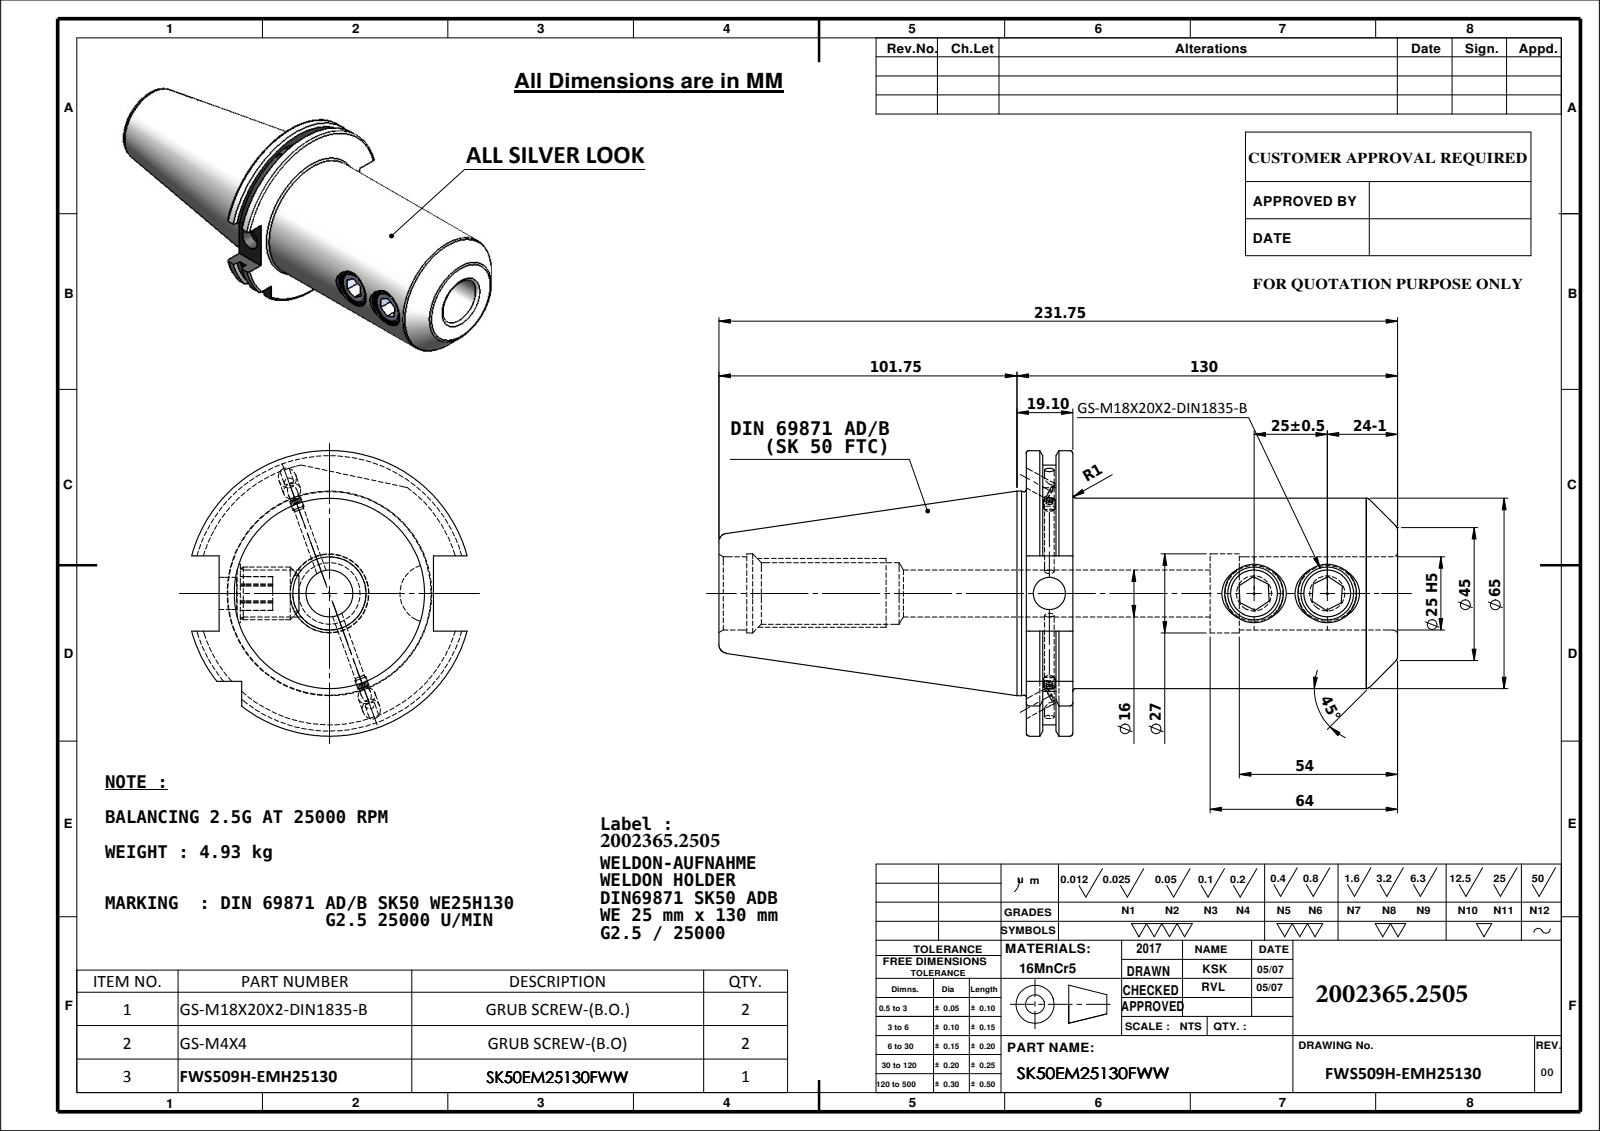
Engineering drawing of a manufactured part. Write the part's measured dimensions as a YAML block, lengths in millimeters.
part_name: "91506-WE725130; Copy of M4X4_DIN 913 - M4 x 4-N; GS-M18X2X20; SK50EM25130FWW"
step_written_by: "SolidWorks 2009 (CONFIG_CONTROL_DESIGN)"
units: millimeters
bodies: {solids: 5, faces: 194, planar: 63, cylindrical: 61, other: 70}
overall_size: [231.75, 97.5, 94.05]
volume: 639632
surface_area: 78382
round_holes:
  - {diameter: 16, count: 3}
  - {diameter: 6, count: 2}
  - {diameter: 20, count: 2}
  - {diameter: 3.3, count: 1}
  - {diameter: 11, count: 1}
  - {diameter: 21, count: 1}
  - {diameter: 25, count: 1}
  - {diameter: 27, count: 1}
round_bosses_or_shafts:
  - {diameter: 18, count: 2}
  - {diameter: 4, count: 2}
  - {diameter: 69.85, count: 1}
  - {diameter: 69.45, count: 1}
  - {diameter: 65, count: 1}
partial_cylinders:
  - {radius: 44.9, count: 1}
  - {radius: 48.75, count: 1}
face_to_face_distances: [15.9, 126.8, 110.9, 10.15, 5.75, 116.65, 5.66, 4.49, 10.24, 121.14]
hole_center_spacings: [25, 69.9, 94.9]
